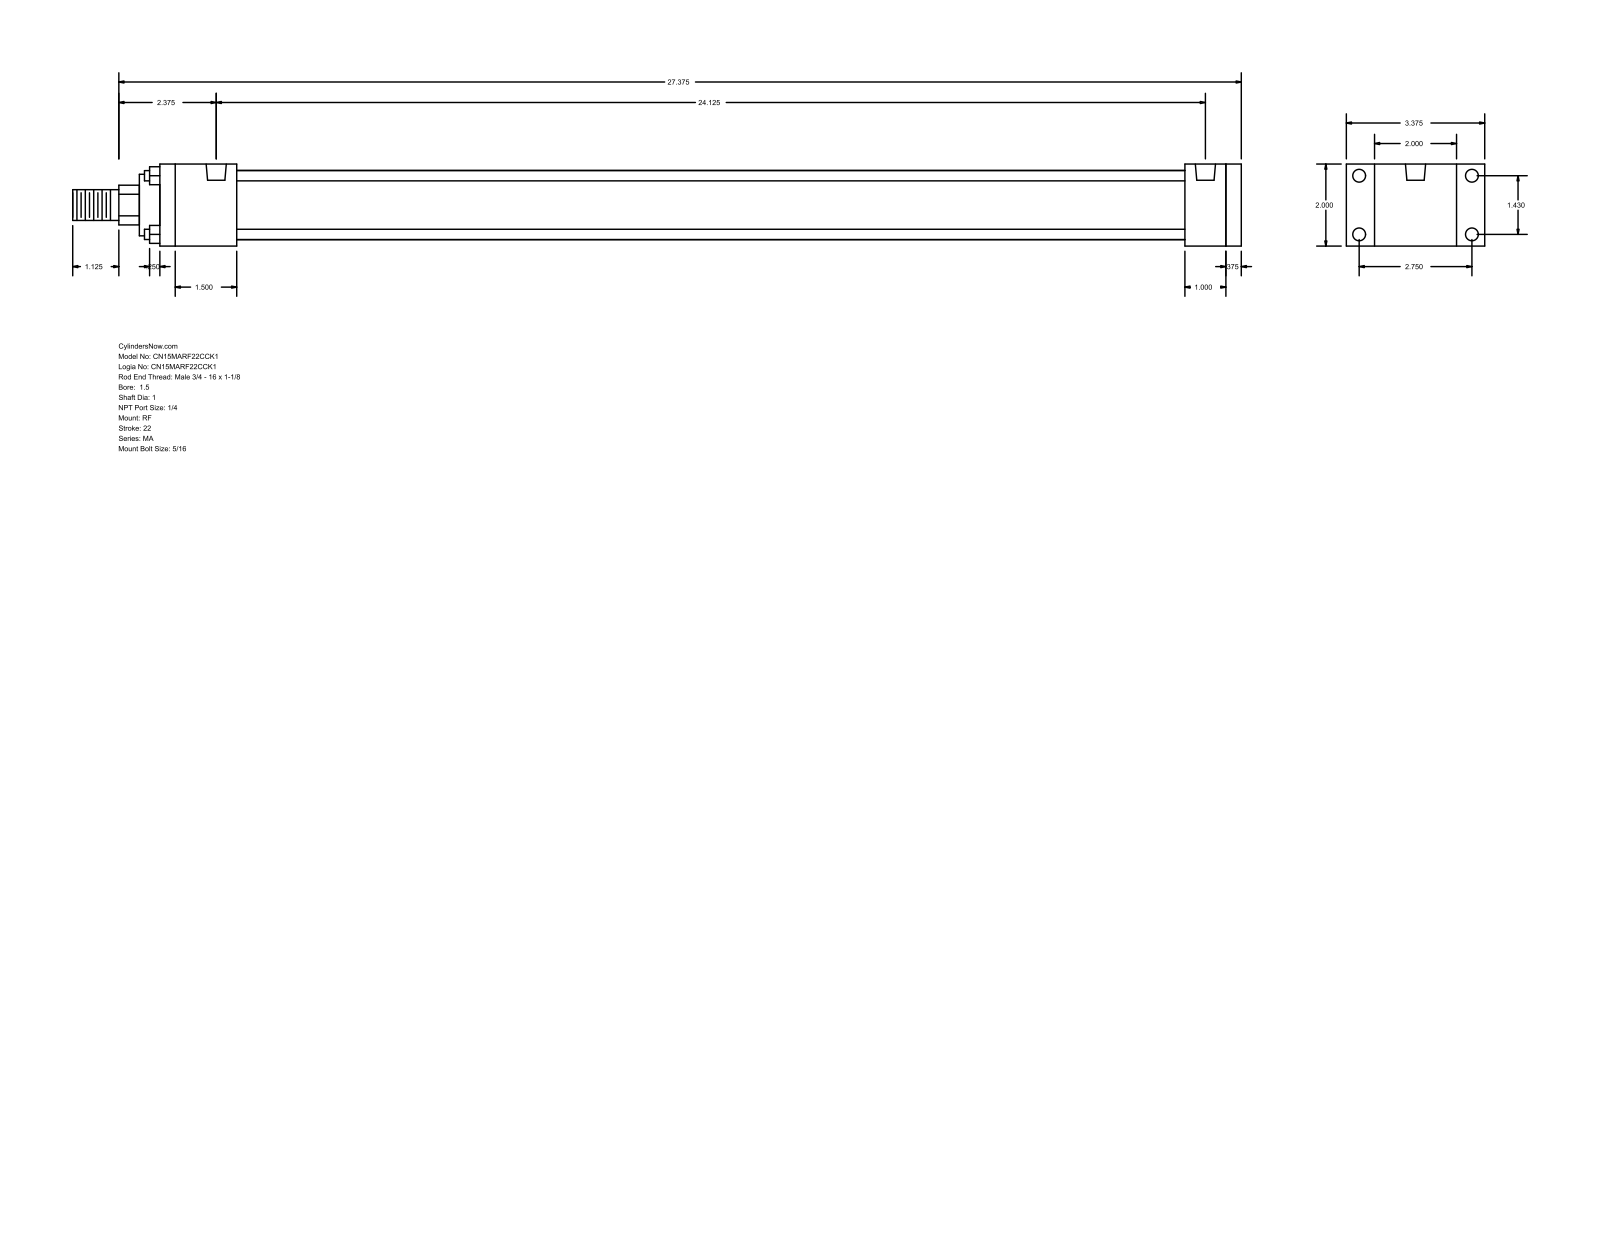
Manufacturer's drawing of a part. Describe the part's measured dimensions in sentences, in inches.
The part is named "MA_RF__0150_1". Its 3-D file was written by "GSSL Pune (CONFIG_CONTROL_DESIGN)". It is 0 solids with 92 faces: 64 planar, 28 cylindrical and 0 other. Overall it measures 28.5 by 3.375 by 2 inches. Round holes: 8 of diameter 0.313, 2 of diameter 0.492. Round bosses or shafts: 4 of diameter 0.25, 1 of diameter 1.69, 1 of diameter 1.5, 1 of diameter 1, 1 of diameter 0.75. Partial cylindrical surfaces (rounded edges, fillets, slot ends): 1 of radius 0.484. The main face-to-face distances are 2, 0.375, 26, 1, 26.375, 25, 1.375, 1.875, 23.125, 24.125. The hole center spacings are 1.43, 2.75, 3.099, 24.125.
